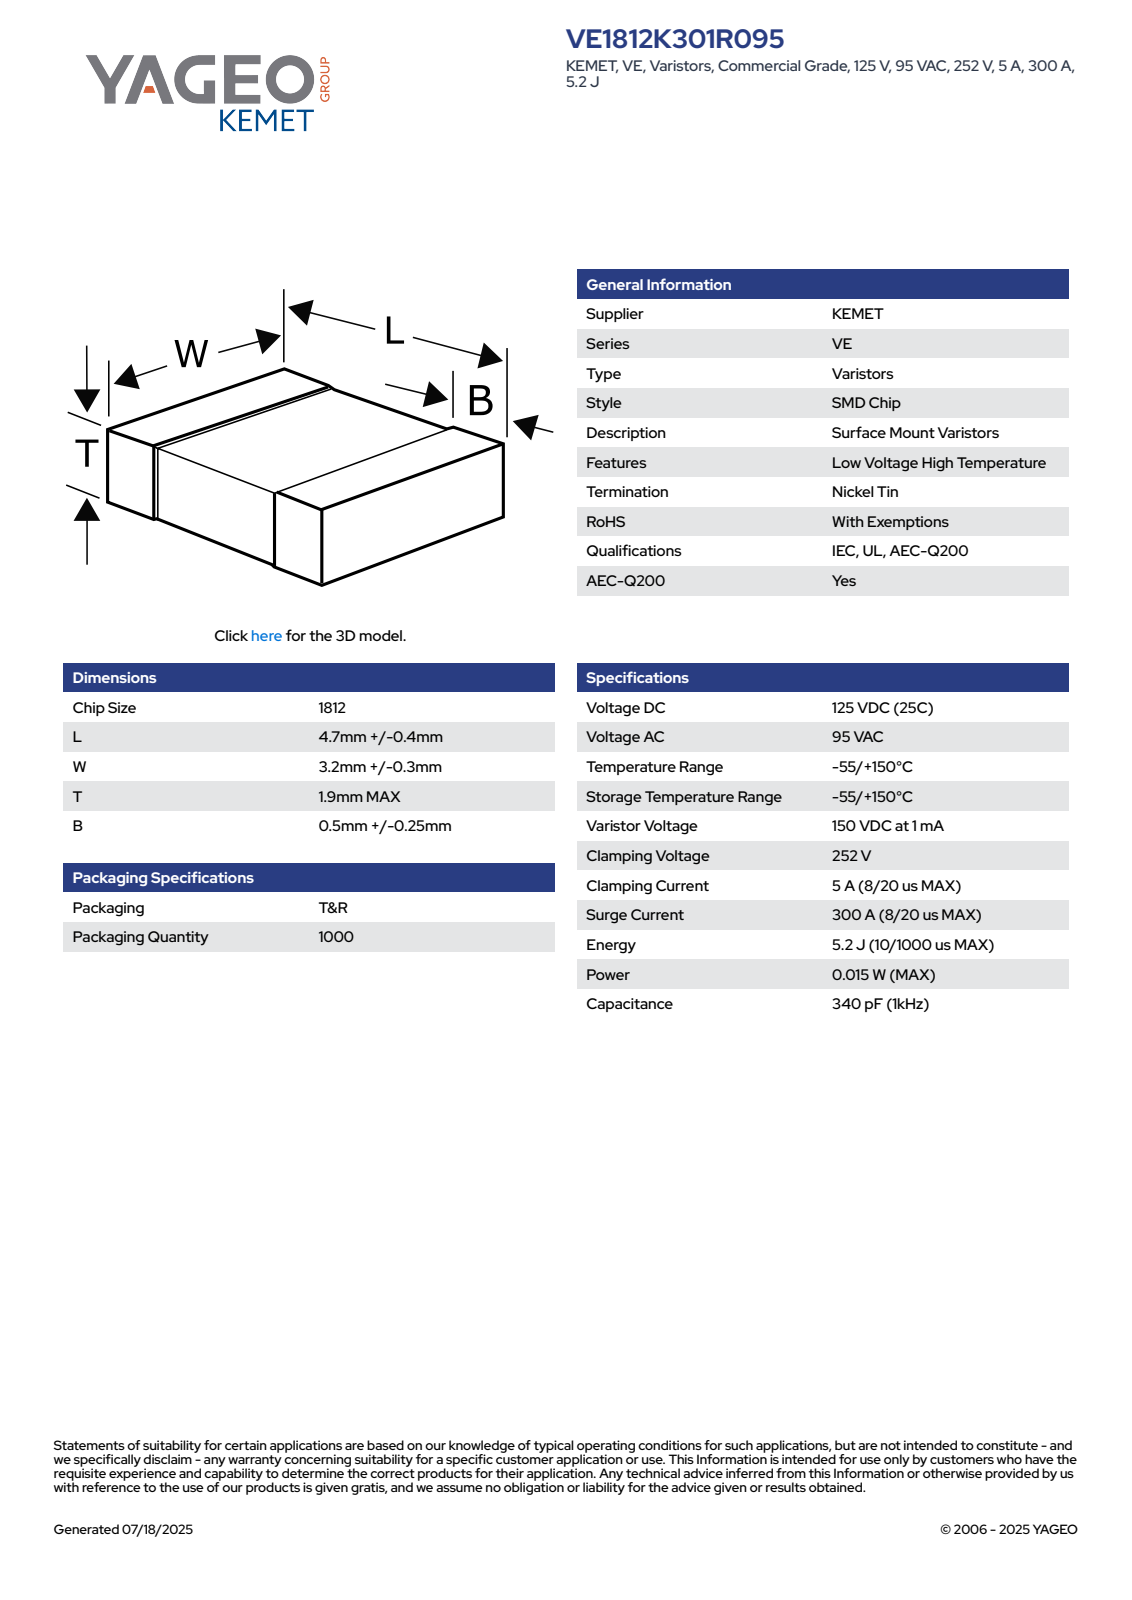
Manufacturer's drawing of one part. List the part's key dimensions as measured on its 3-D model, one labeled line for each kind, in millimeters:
Part name (STEP PRODUCT): VS_SMD_1812_L5.1W3.5T1.9B0.75
STEP written by: SolidWorks 2021 (AUTOMOTIVE_DESIGN)
Units: millimetres
Bodies: 4 solids, 129 faces (71 planar, 42 cylindrical, 16 other)
Overall size (bounding box): 5.1 × 3.5 × 1.9
Volume: 31 mm³ · Surface area: 67 mm²
Main face-to-face distances: 1.76, 1.83, 5.1, 3.36, 3.43, 1.9, 3.5, 2.24, 2.86, 2.75
